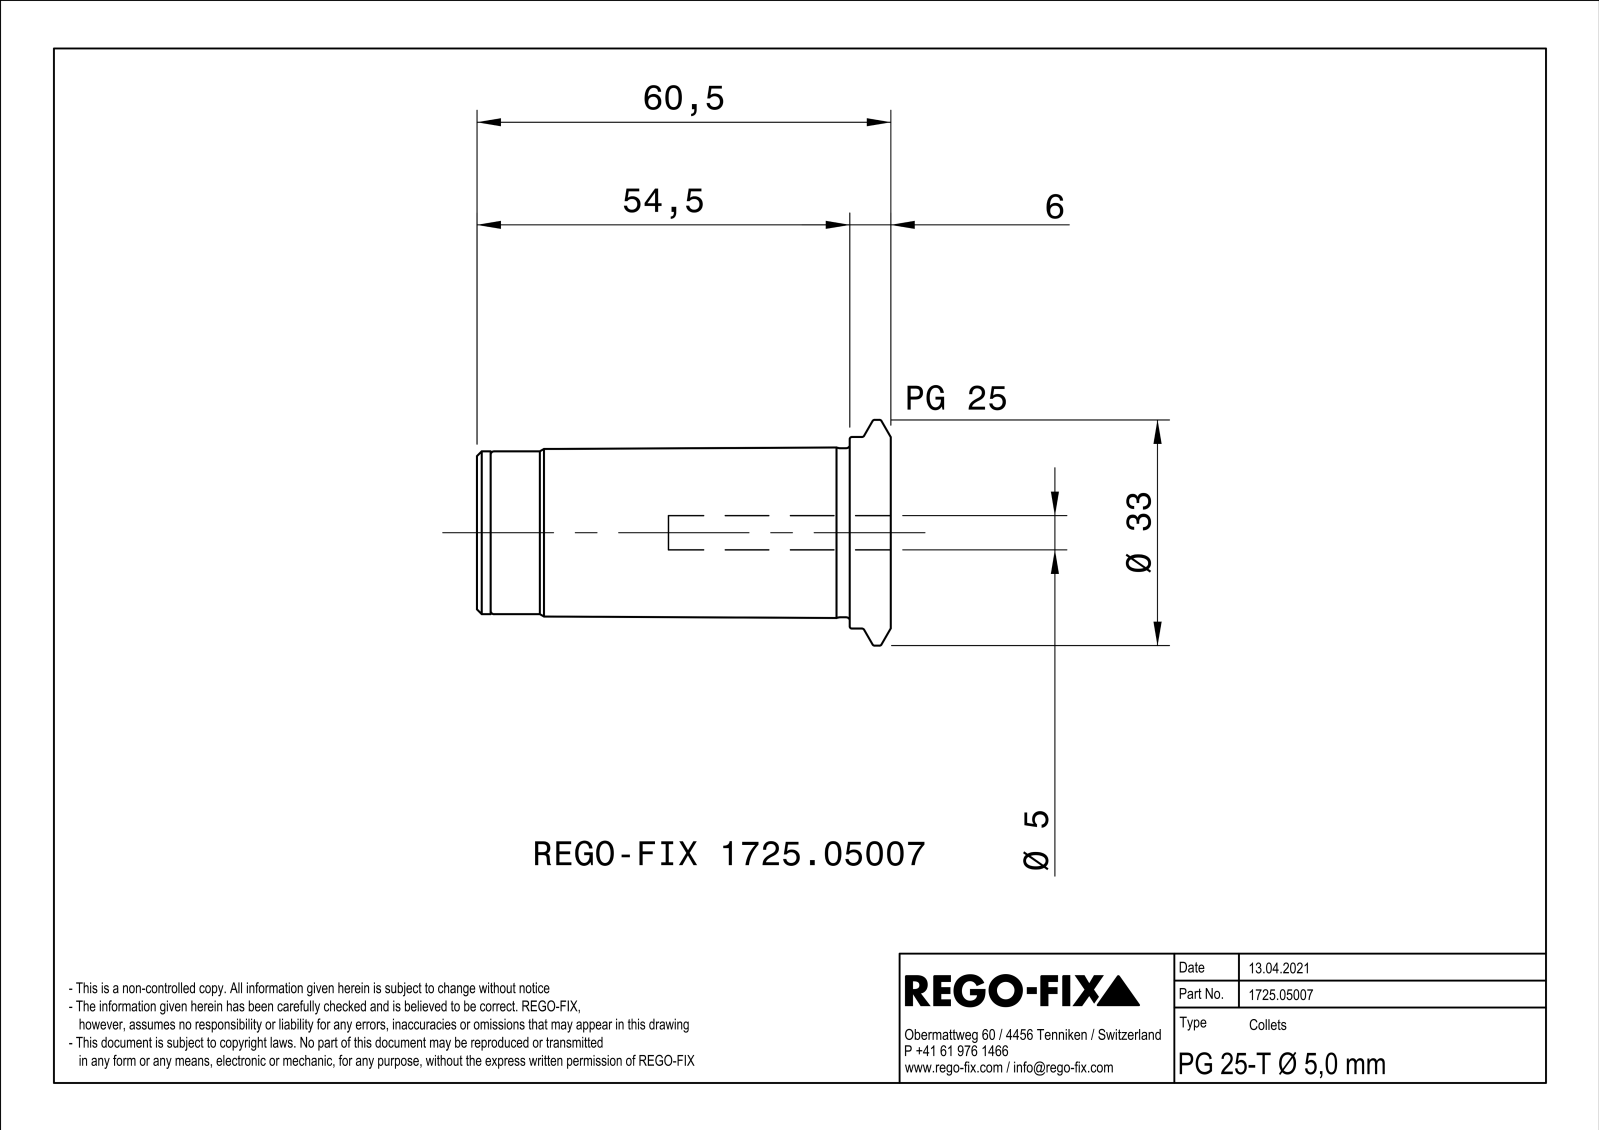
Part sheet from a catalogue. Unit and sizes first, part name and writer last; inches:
Units: inches
Overall size (bounding box): 2.303 × 1.299 × 1.297
Round holes (diameter × count): ⌀0.128 ×1, ⌀0.169 ×1, ⌀0.197 ×1, ⌀0.354 ×1, ⌀0.827 ×1, ⌀0.866 ×1
Round bosses / shafts (diameter × count): ⌀1.299 ×1, ⌀1.102 ×1, ⌀0.972 ×1, ⌀0.937 ×1
Partial cylindrical surfaces — rounded edges, fillets, slot ends (radius × count): R0.02 ×2, R0.16 ×1, R0.164 ×1
Main face-to-face distances: 0.039, 0.236, 2.201, 2.244, 1.965, 2.008, 0.043, 2.303, 2.067, 0.102
Bodies: 0 solids, 88 faces (24 planar, 23 cylindrical, 41 other)
Part name (STEP PRODUCT): NOCUT
STEP written by: SIEMENS PLM Software Solid Edge ST10 (AUTOMOTIVE_DESIGN)
